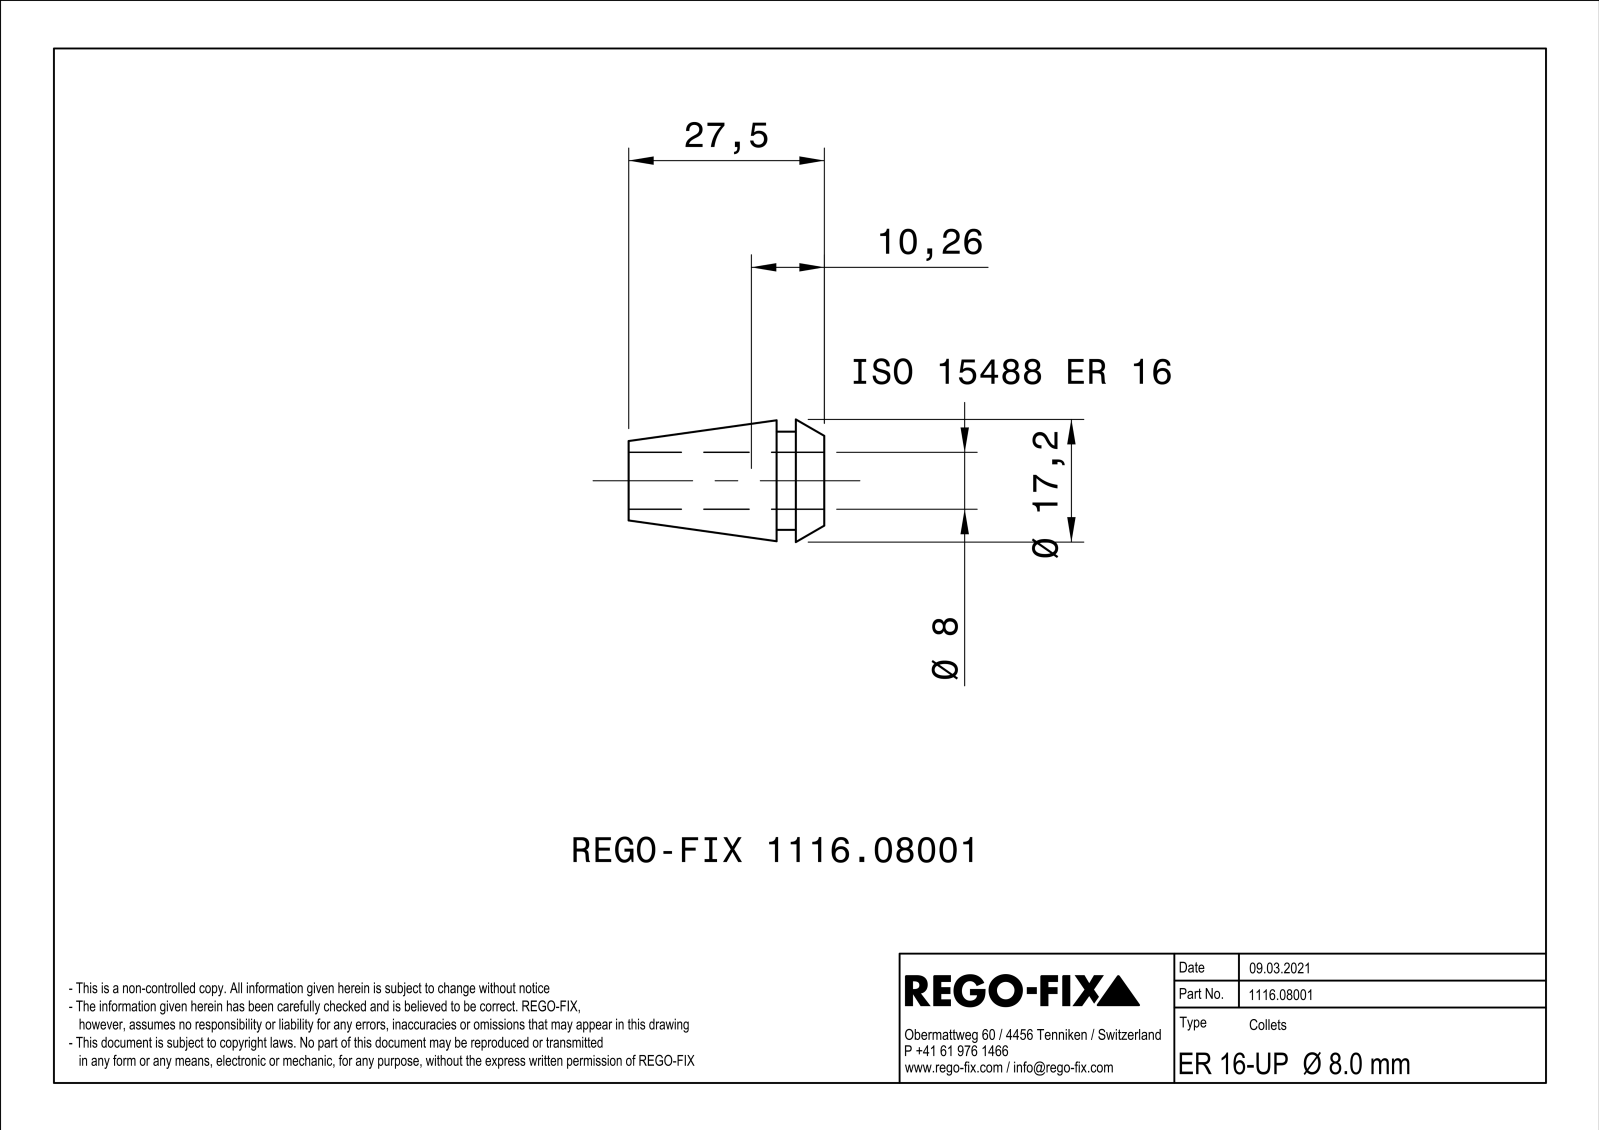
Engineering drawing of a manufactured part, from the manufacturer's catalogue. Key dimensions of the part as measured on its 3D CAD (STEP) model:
Part name (STEP PRODUCT): NOCUT
STEP written by: SIEMENS PLM Software Solid Edge ST10 (AUTOMOTIVE_DESIGN)
Units: millimetres
Bodies: 1 solid, 153 faces (72 planar, 25 cylindrical, 56 other)
Overall size (bounding box): 27.5 × 17.24 × 17.24
Volume: 2 289 mm³ · Surface area: 4 144 mm²
Round holes (diameter × count): ⌀8 ×1
Round bosses / shafts (diameter × count): ⌀13.8 ×1
Partial cylindrical surfaces — rounded edges, fillets, slot ends (radius × count): R0.3 ×8
Main face-to-face distances: 0.6, 4, 6.7, 2.7, 27.5, 23.5, 20.8
